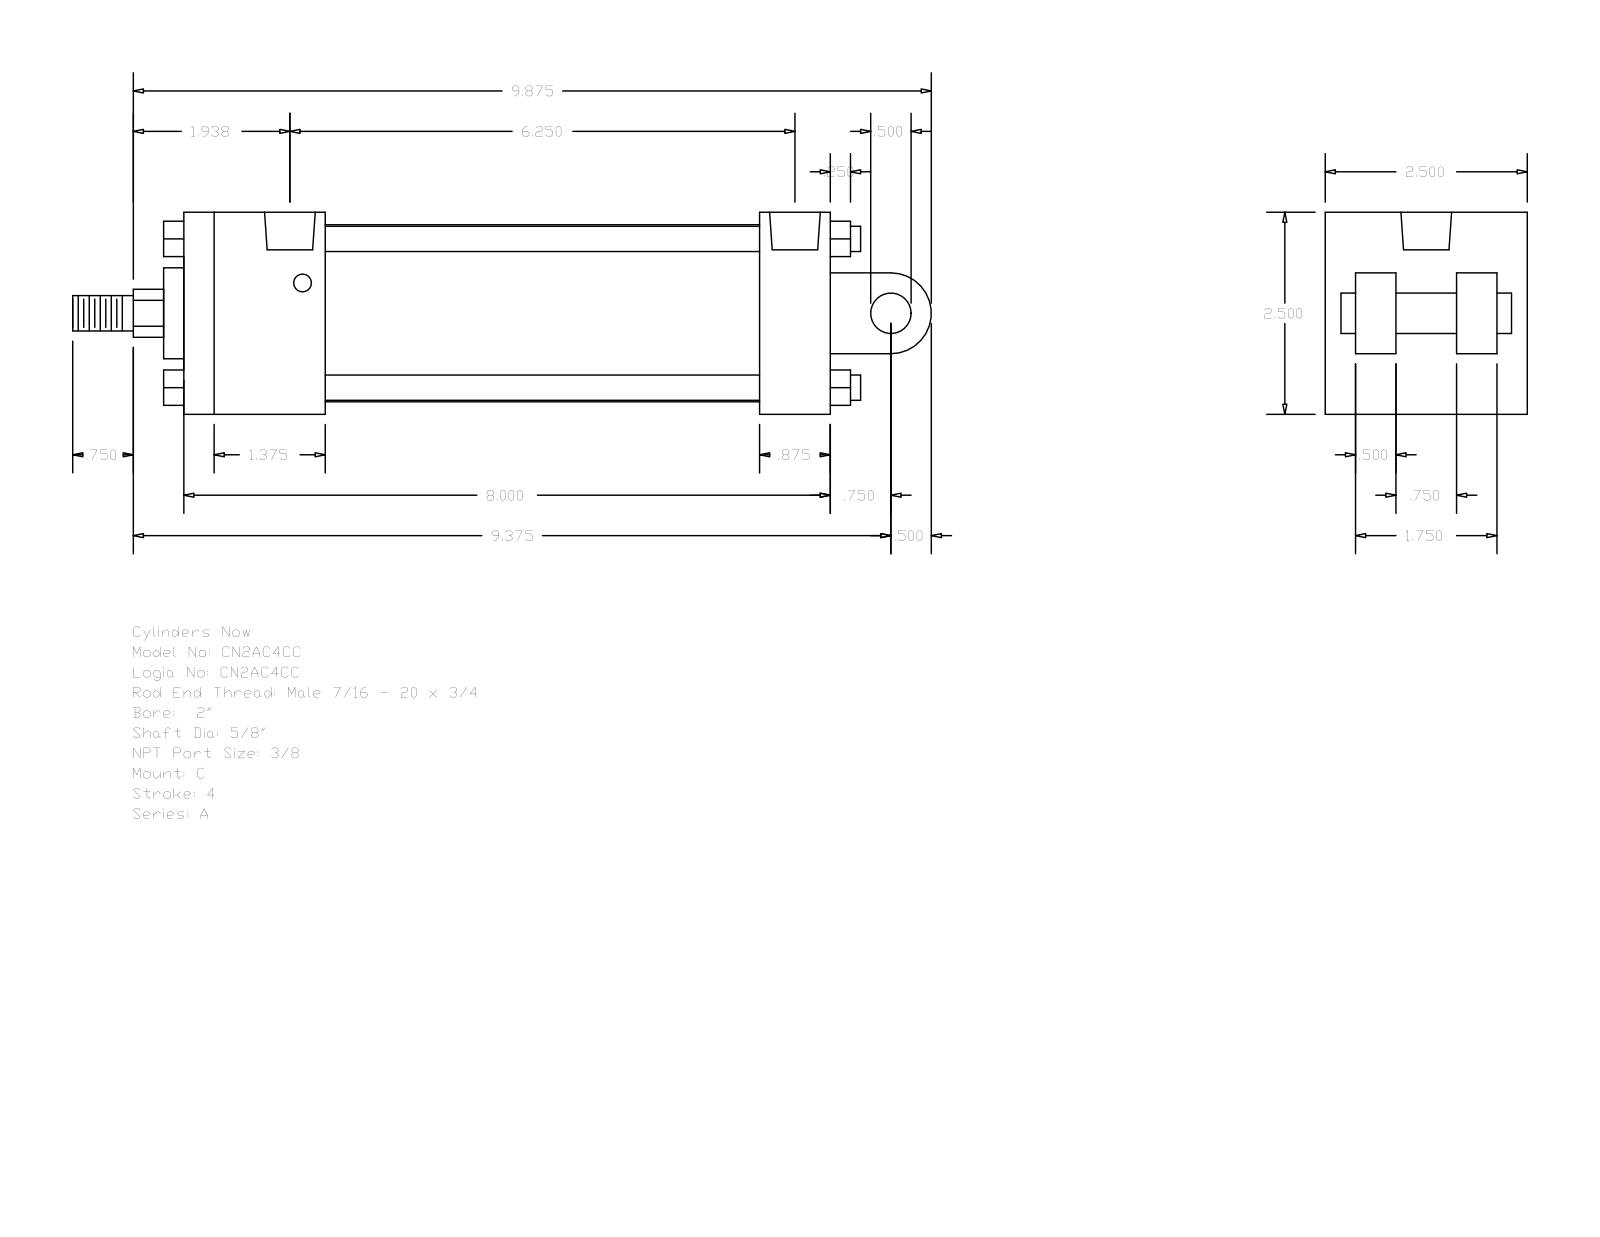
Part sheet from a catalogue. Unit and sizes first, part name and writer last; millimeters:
Units: millimetres
Overall size (bounding box): 269.88 × 63.5 × 63.5
Round holes (diameter × count): ⌀5.56 ×4, ⌀15.93 ×2
Round bosses / shafts (diameter × count): ⌀7.94 ×4, ⌀55.63 ×1, ⌀28.57 ×1, ⌀15.88 ×1, ⌀12.7 ×1, ⌀11.11 ×1
Partial cylindrical surfaces — rounded edges, fillets, slot ends (radius × count): R7.54 ×1, R12.7 ×1
Main face-to-face distances: 63.5, 203.19, 22.22, 44.45, 158.74, 180.97, 136.52, 12.7, 53.98, 19.05
Hole centre spacings: 150.8, 3.97, 3.98, 154.77, 154.78, 158.75
Bodies: 0 solids, 135 faces (102 planar, 33 cylindrical, 0 other)
Part name (STEP PRODUCT): A_C__0200_0.625
STEP written by: GSSL Pune (CONFIG_CONTROL_DESIGN)
